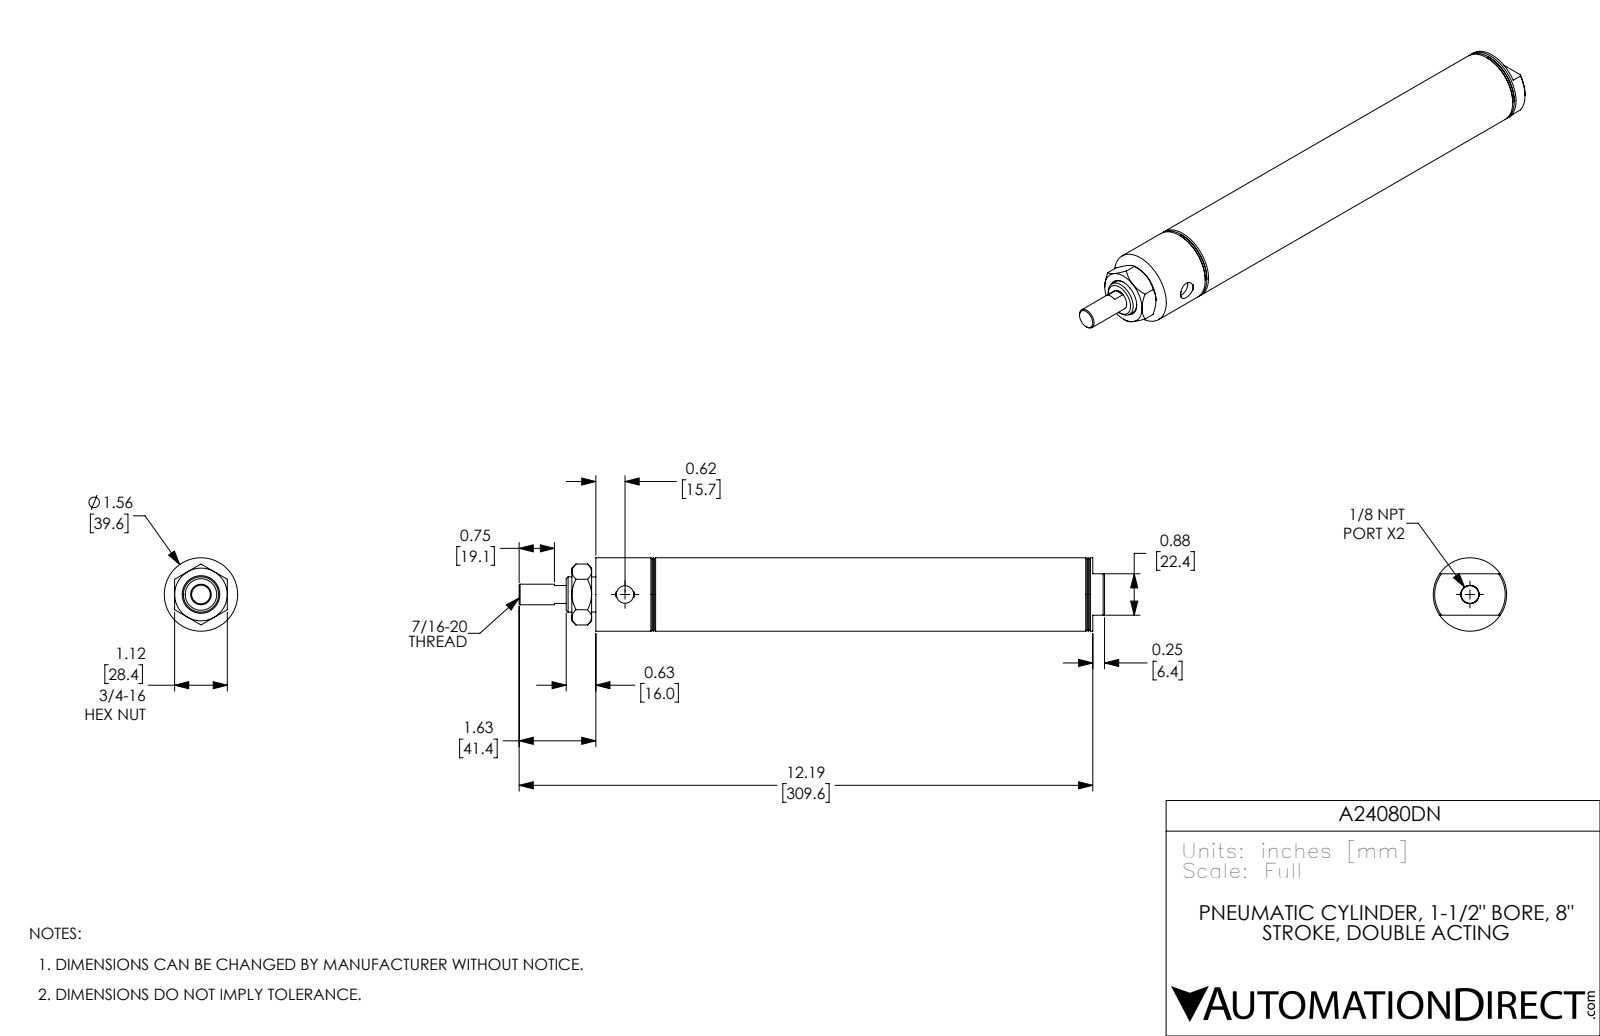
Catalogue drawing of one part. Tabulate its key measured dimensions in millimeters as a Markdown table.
| quantity | value |
| --- | --- |
| part name | A24080DN; A24080DN_Mounting Nut_D-3556; A24080DN-Rod; A24080DN-MainBody |
| STEP written by | SolidWorks 2017 (AUTOMOTIVE_DESIGN) |
| units | millimeters |
| bodies | 3 solids, 104 faces (32 planar, 24 cylindrical, 48 other) |
| overall size | 316 × 39.6 × 39.6 |
| volume | 134 400 mm³ |
| surface area | 83 550 mm² |
| round holes (diameter × count) | 9.5 × 2, 11.1 × 1, 19.1 × 1, 38.1 × 1 |
| round bosses / shafts (diameter × count) | 39.6 × 1, 18.9 × 1 |
| main face-to-face distances | 215.9, 12.7, 203.2, 249.9, 237.2, 34, 24.6, 37.3, 240.5, 274.6 |
